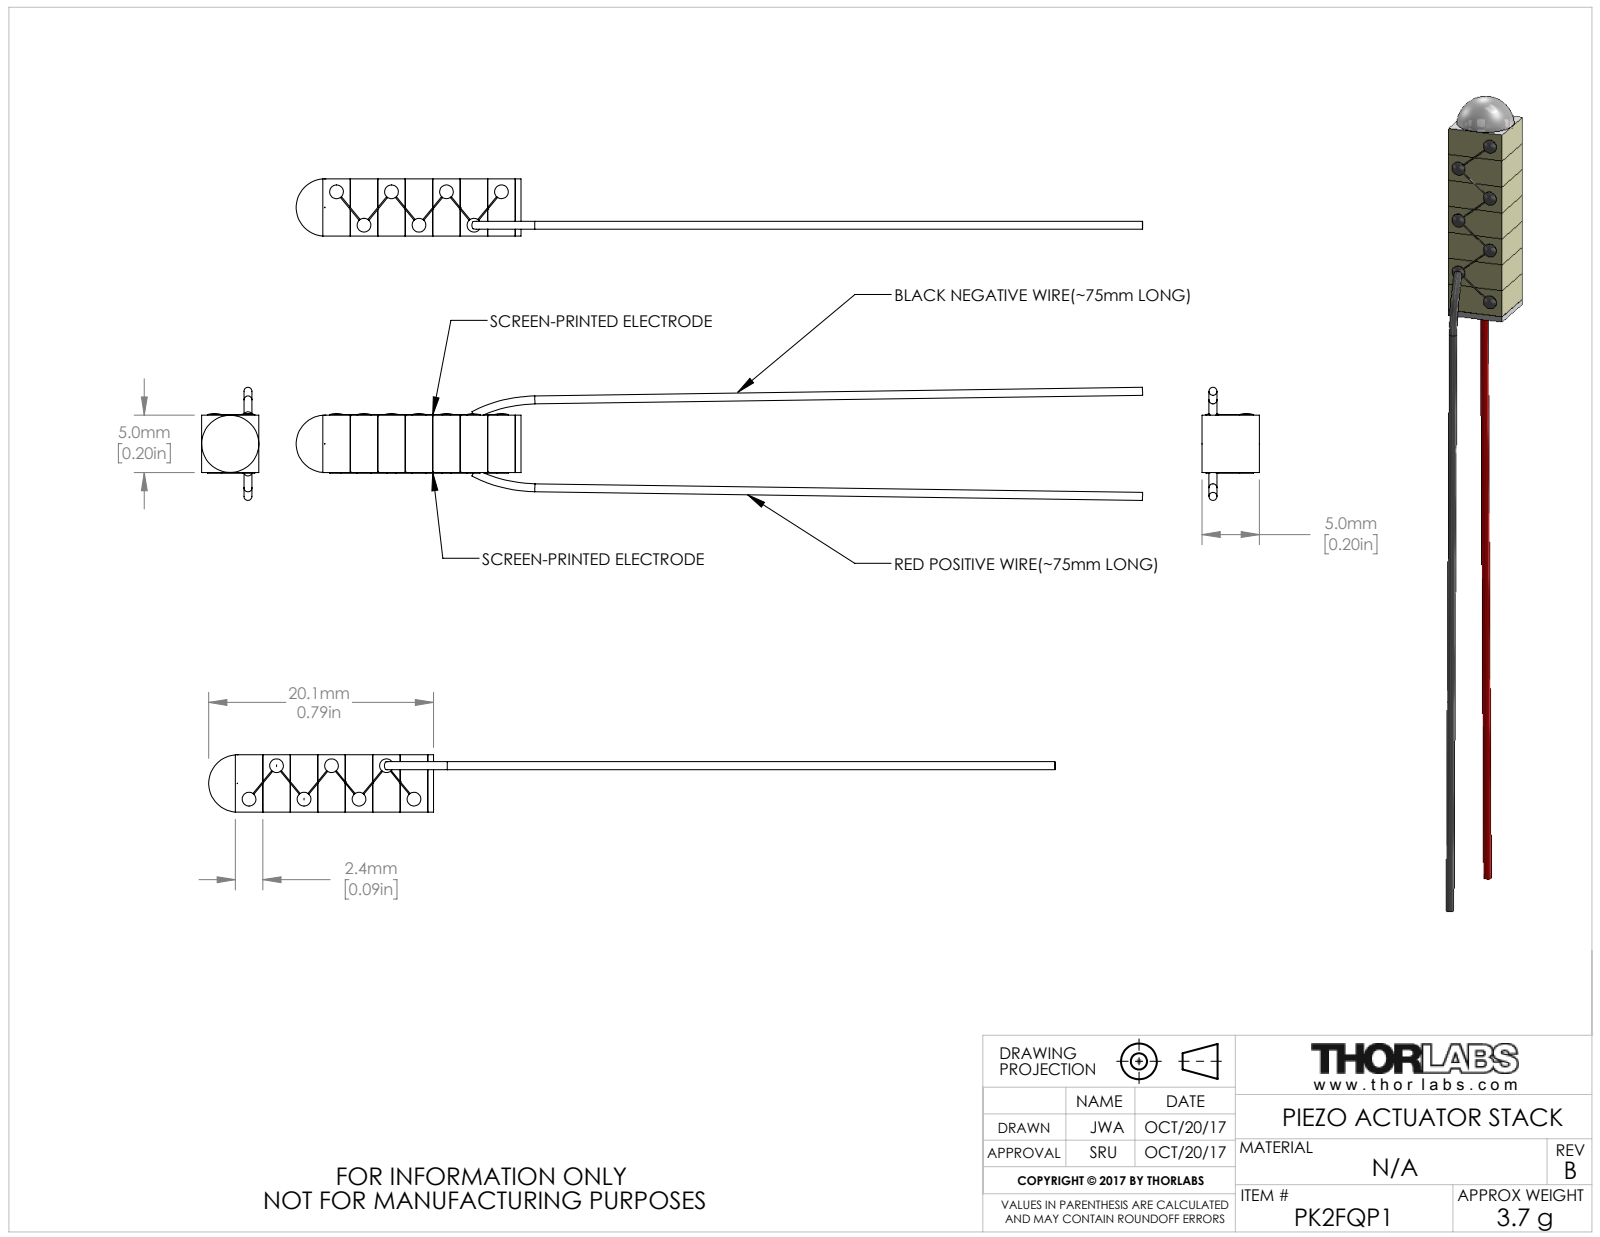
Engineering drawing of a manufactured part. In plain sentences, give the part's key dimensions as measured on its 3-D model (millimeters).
The part is named "CTN002574". Its 3-D file was written by "SolidWorks 2016 (AUTOMOTIVE_DESIGN)". It is 8 solids with 170 faces: 75 planar, 66 cylindrical and 29 other. Overall it measures 73.9 by 9.87 by 5 millimeters. Its volume is 479 cubic millimeters and its surface area 1 092 square millimeters. Round bosses or shafts: 7 of diameter 1.2, 2 of diameter 0.7. The main face-to-face distances are 2.4, 4.8, 7.2, 5, 9.6, 12, 14.4, 0.5, 2.91, 5.31.
